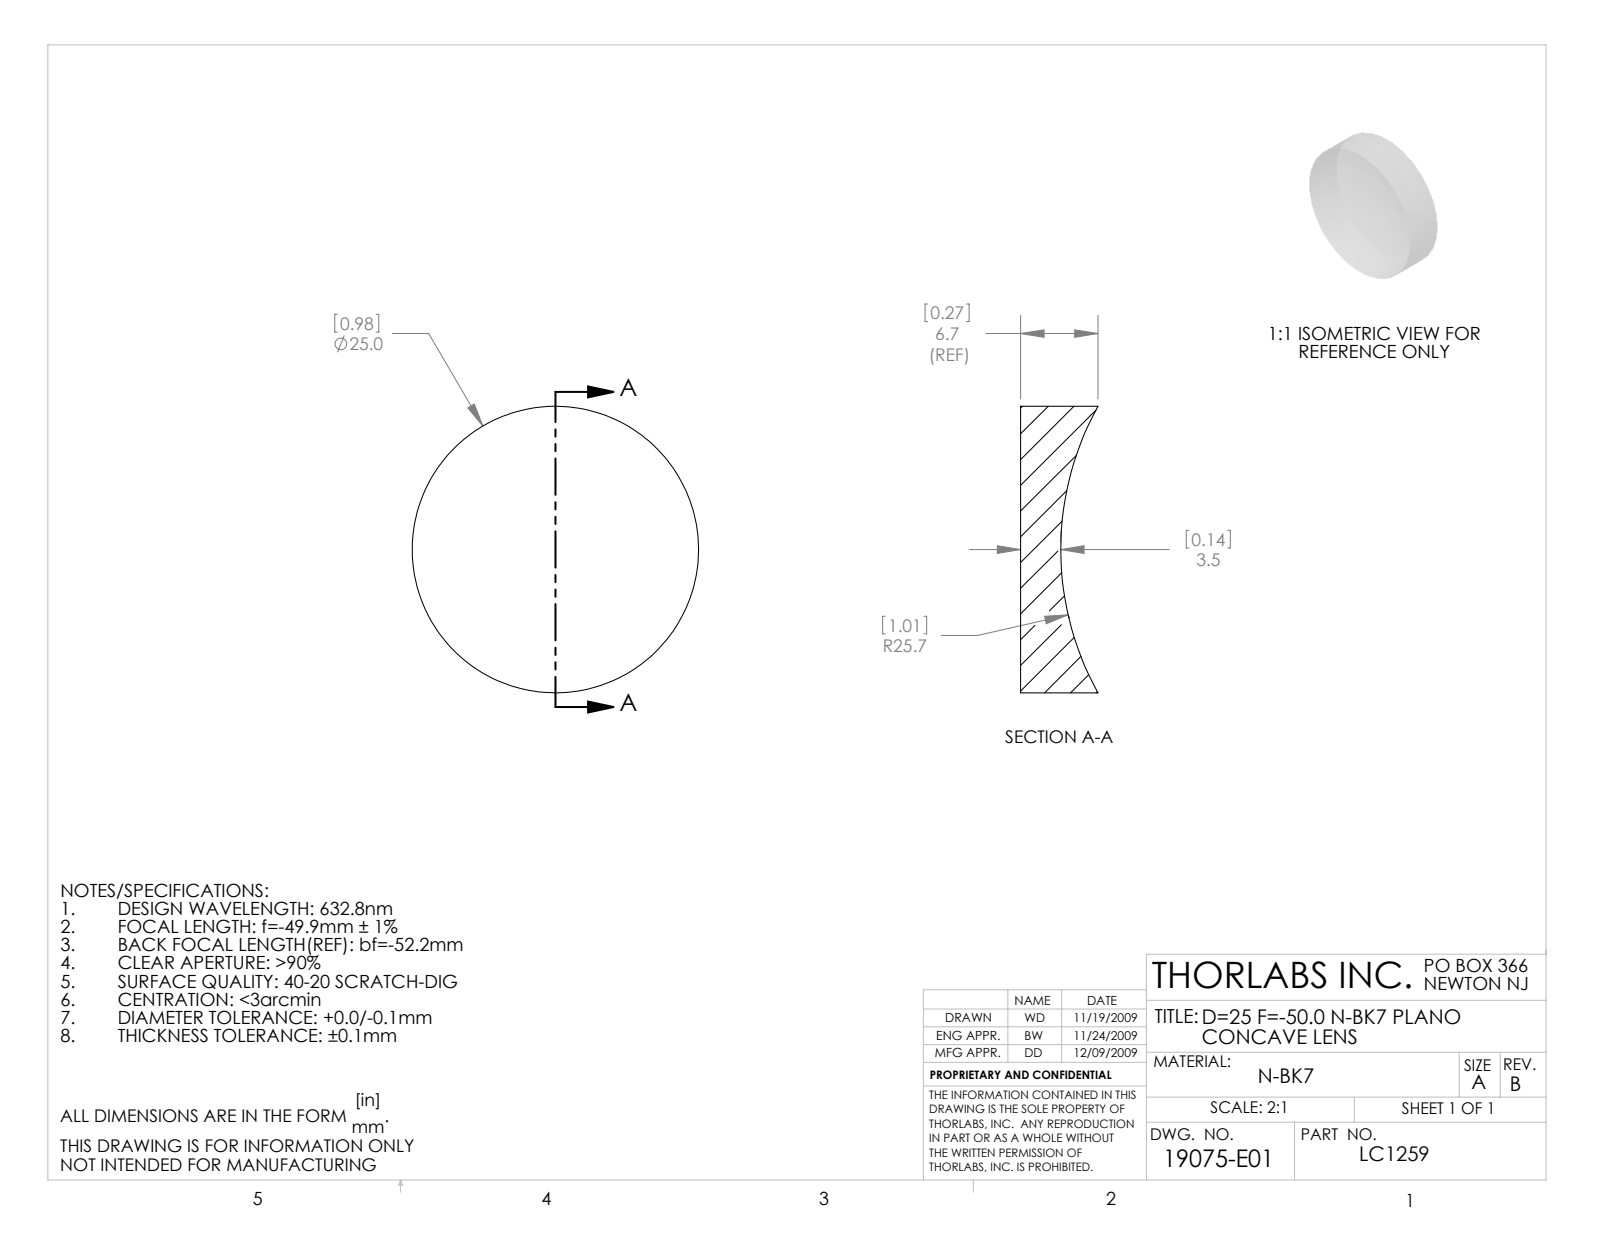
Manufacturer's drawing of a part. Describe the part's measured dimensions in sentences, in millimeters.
The part is named "19075-E0W". Its 3-D file was written by "SolidWorks 2009 (AUTOMOTIVE_DESIGN)". It is 1 solid with 5 faces: 1 planar, 2 cylindrical and 2 other. Overall it measures 25 by 25 by 6.75 millimeters. Its volume is 2 497 cubic millimeters and its surface area 1 545 square millimeters. Round bosses or shafts: 1 of diameter 25.
